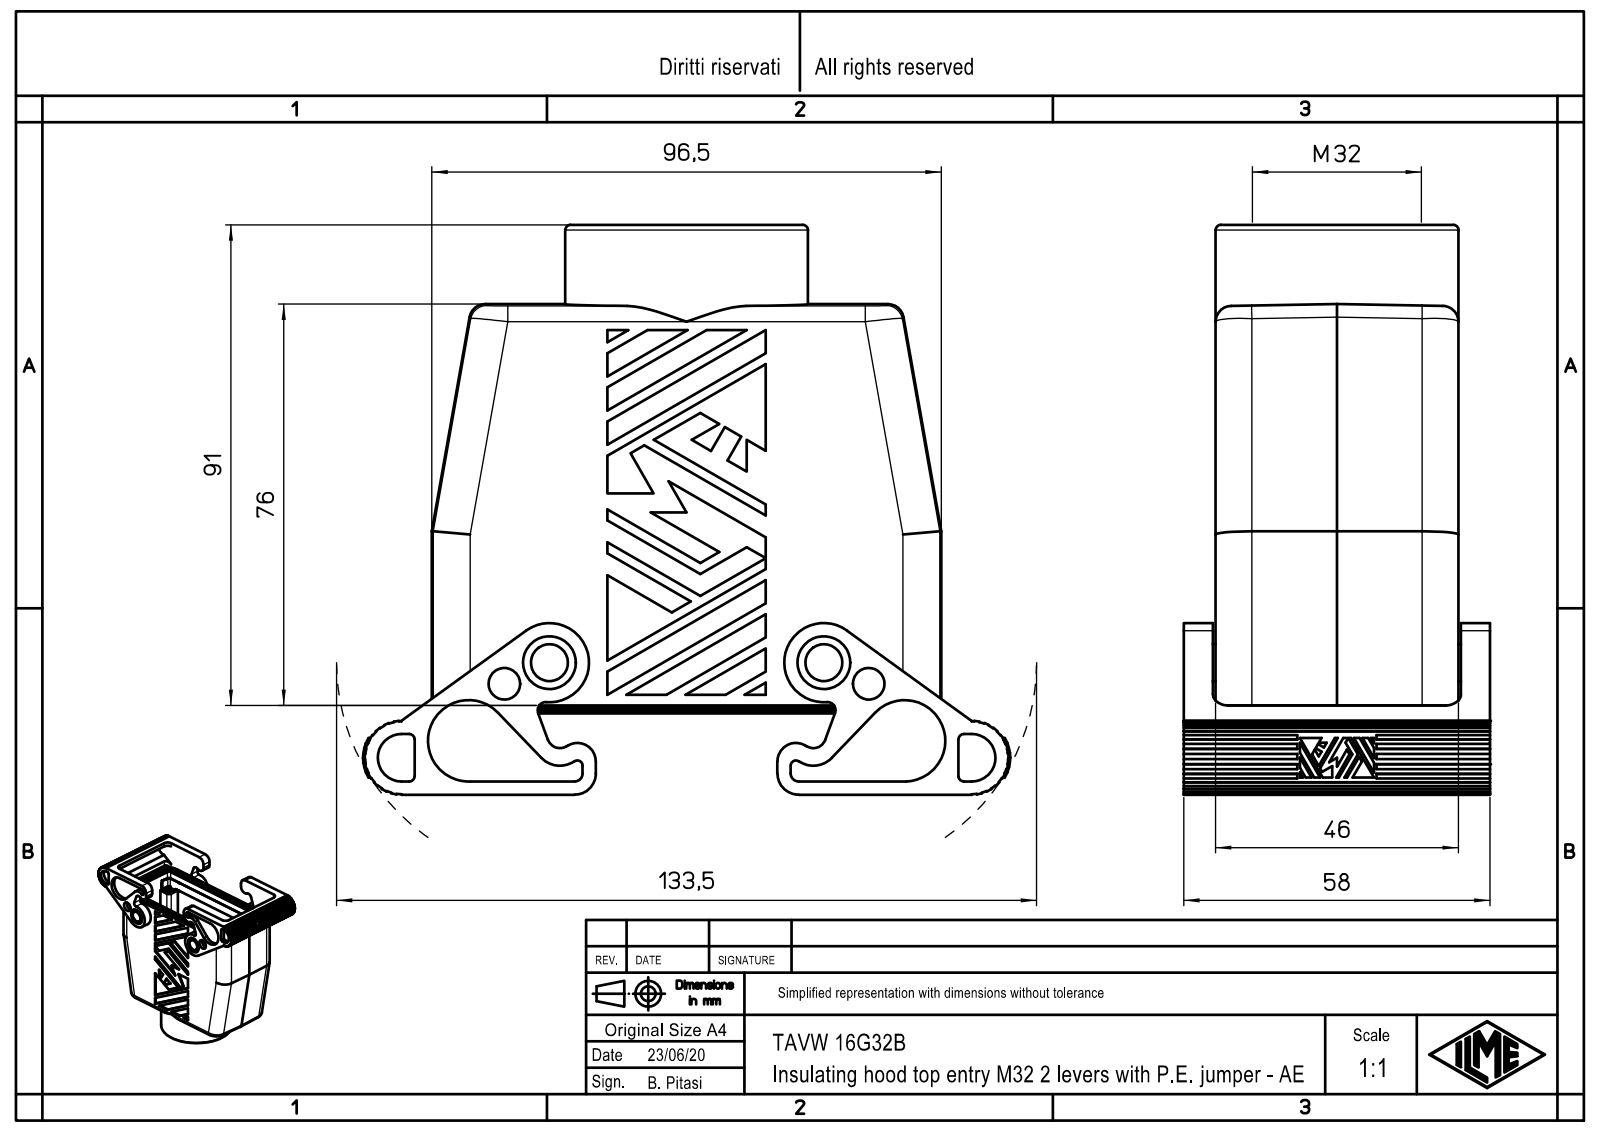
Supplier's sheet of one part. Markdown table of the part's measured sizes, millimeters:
| quantity | value |
| --- | --- |
| part name | TAVW_16G32B |
| STEP written by | Creo Elements/Direct Modeling 20.1B 02-Apr-2019 (C) Parametric Technology GmbH (AUTOMOTIVE_DESIGN) |
| units | millimeters |
| bodies | 1 solid, 799 faces (533 planar, 238 cylindrical, 28 other) |
| overall size | 122.6 × 107.9 × 58 |
| volume | 159 407 mm³ |
| surface area | 68 768 mm² |
| round holes (diameter × count) | 3.5 × 4, 5.12 × 4, 6.5 × 4, 6 × 2, 10 × 2, 28 × 1, 32 × 1 |
| round bosses / shafts (diameter × count) | 7 × 2, 46 × 1 |
| partial cylindrical surfaces (radius × count) | 1.5 × 16, 3 × 10, 7 × 10, 1 × 8, 1.81 × 8, 2 × 8, 1.3 × 4, 1.6 × 4 |
| main face-to-face distances | 46, 0.5, 46.5, 1, 45.5, 2.5, 5.5, 6, 6.5, 51.5 |
| hole center spacings | 41.03, 9.39, 27, 60.63, 77.5, 82.07, 52, 69 |
